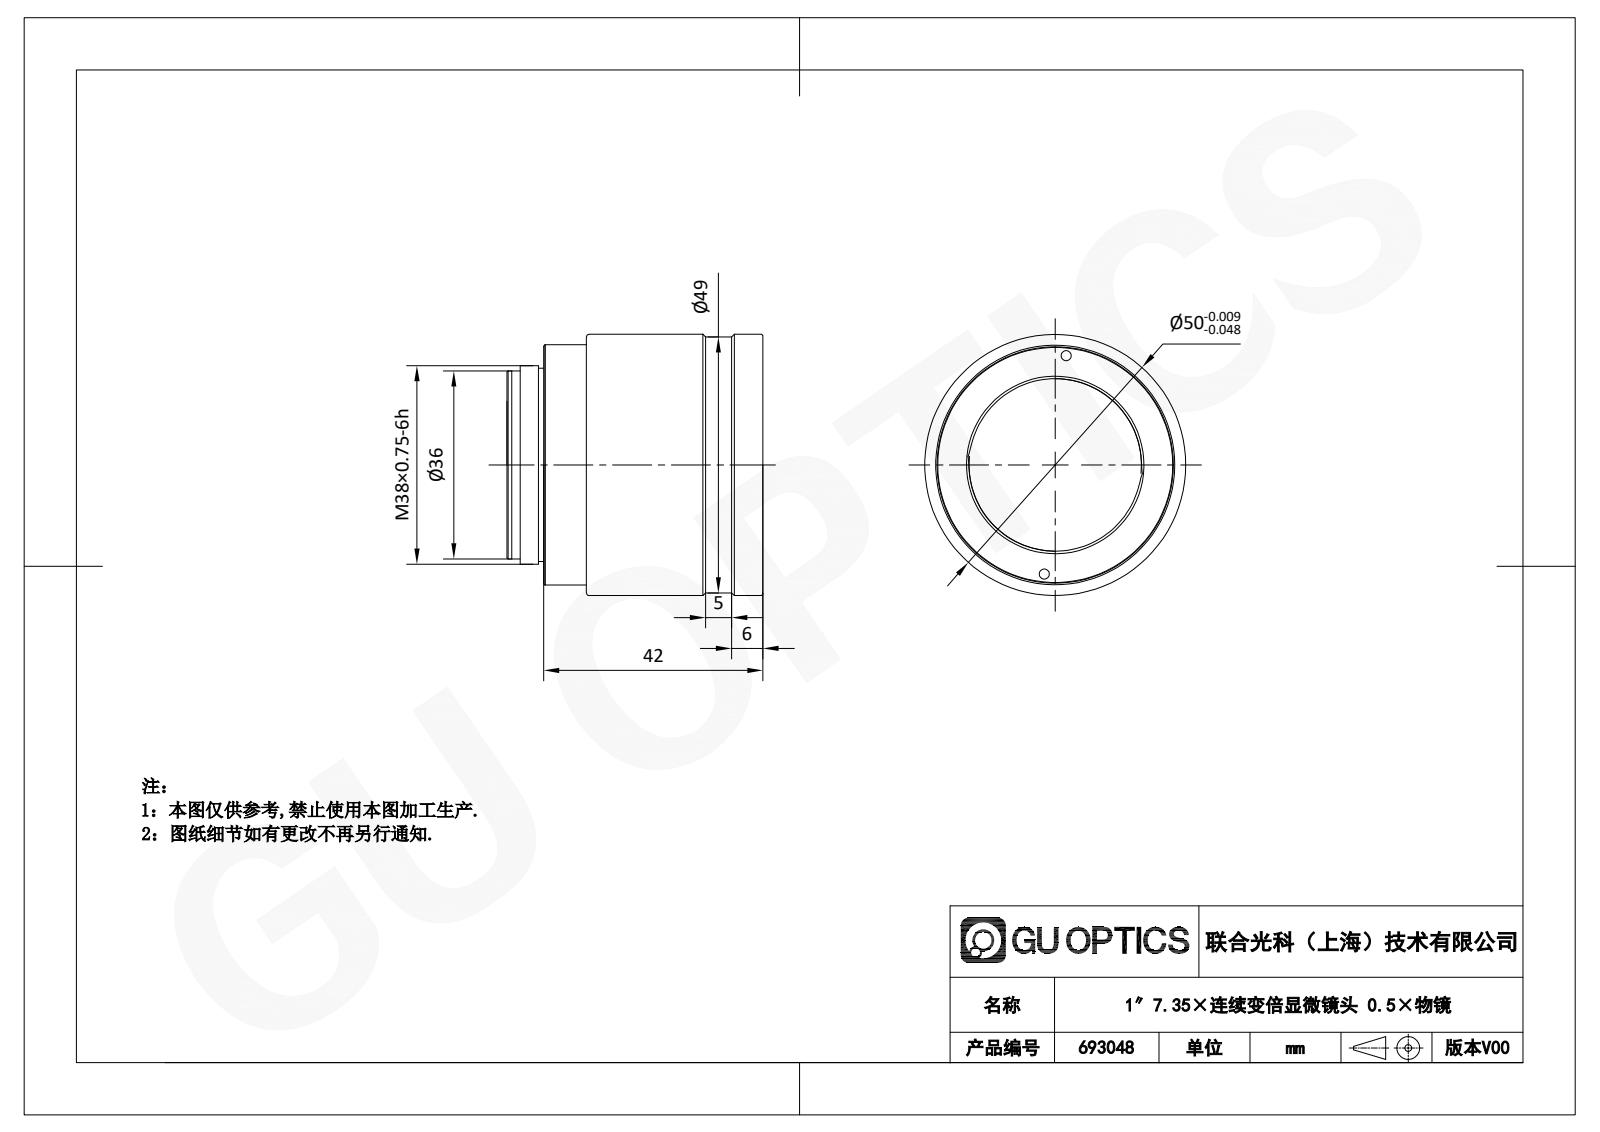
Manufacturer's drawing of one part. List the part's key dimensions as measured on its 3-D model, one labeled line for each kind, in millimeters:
Part name (STEP PRODUCT): 693048
STEP written by: SolidWorks 2020 (CONFIG_CONTROL_DESIGN)
Units: millimetres
Bodies: 0 solids, 58 faces (9 planar, 14 cylindrical, 35 other)
Overall size (bounding box): 50 × 50 × 49
Round holes (diameter × count): ⌀2 ×2, ⌀37 ×1, ⌀45.25 ×1
Round bosses / shafts (diameter × count): ⌀50 ×1, ⌀49 ×1, ⌀46 ×1, ⌀38 ×1, ⌀36 ×1, ⌀34 ×1
Partial cylindrical surfaces — rounded edges, fillets, slot ends (radius × count): R16.5 ×1
Main face-to-face distances: 7.9, 12.7, 4.8, 29.96, 37.86, 42.66, 38.16, 8.2, 4.5, 3.84
Hole centre spacings: 21, 42.01
